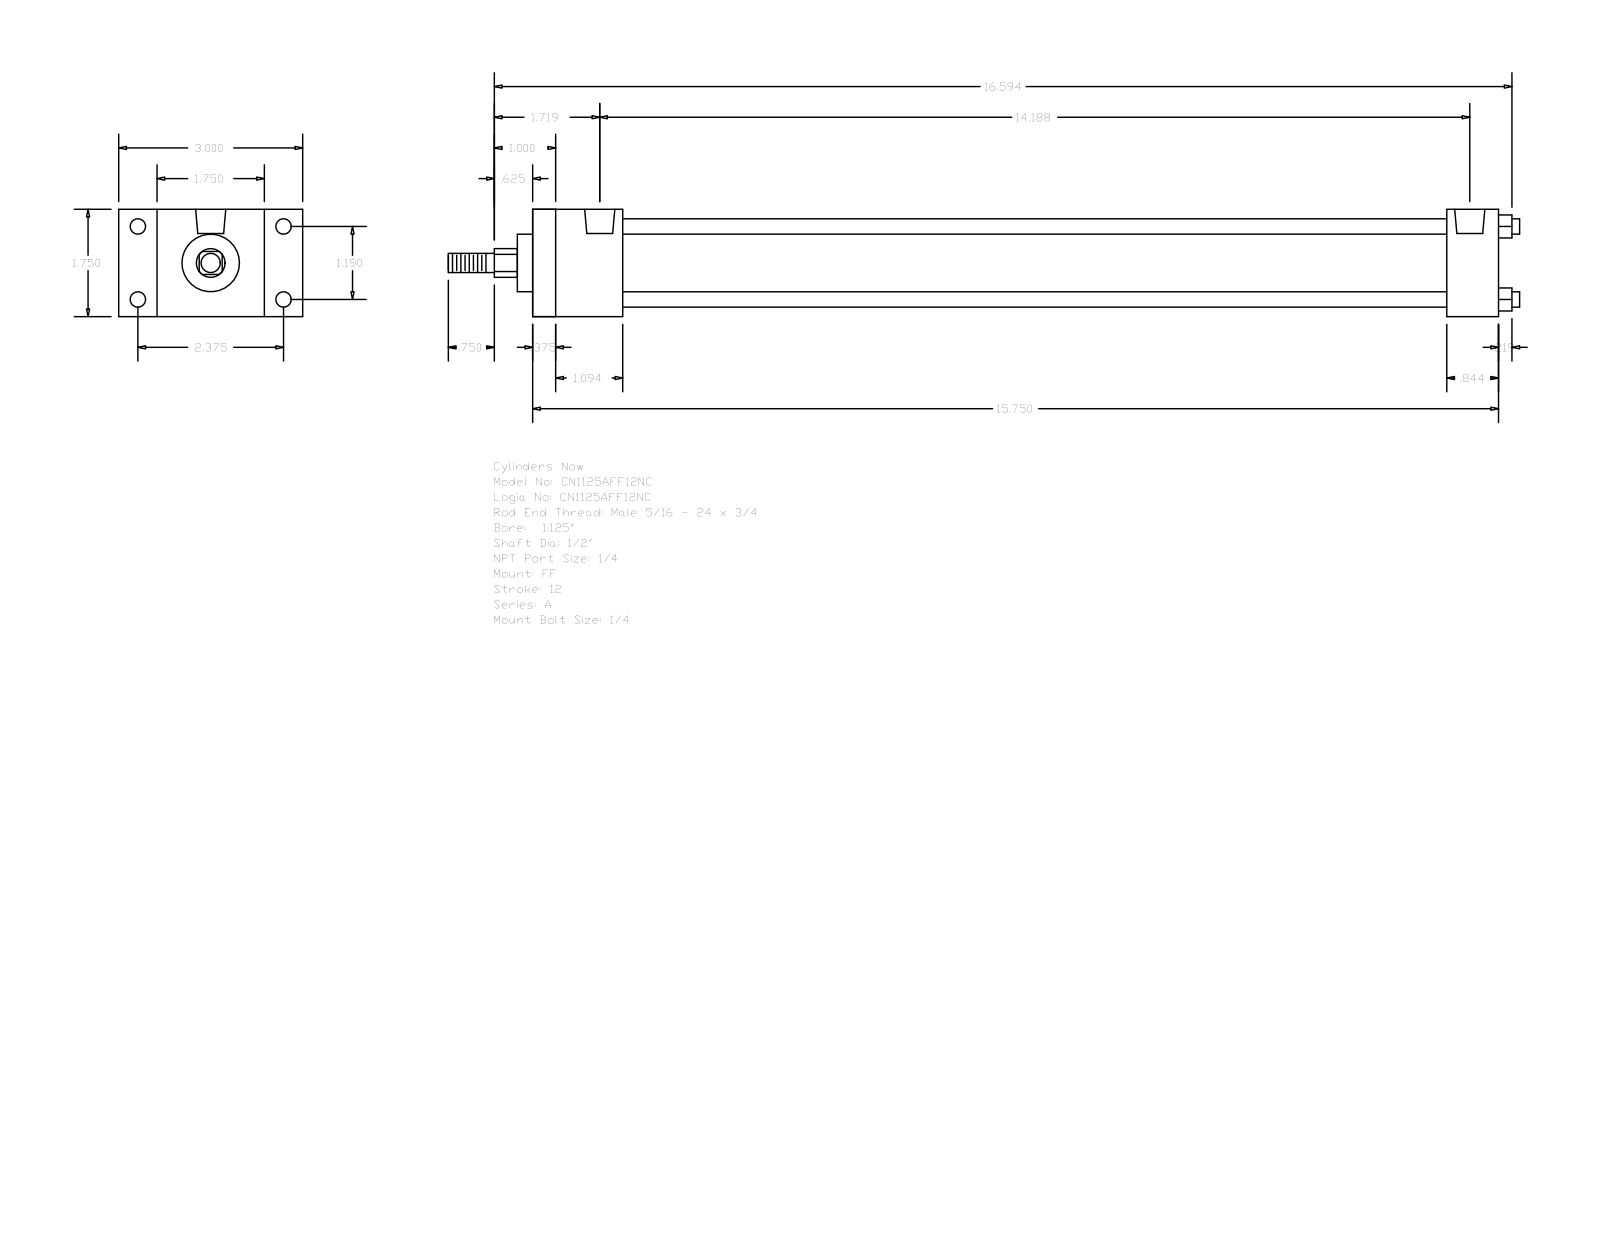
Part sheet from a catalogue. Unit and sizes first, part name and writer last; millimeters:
Units: millimetres
Overall size (bounding box): 443.71 × 76.2 × 44.45
Round holes (diameter × count): ⌀5.56 ×4, ⌀6.35 ×4, ⌀12.49 ×2
Round bosses / shafts (diameter × count): ⌀6.35 ×4, ⌀31.88 ×1, ⌀23.81 ×1, ⌀12.7 ×1, ⌀7.94 ×1
Partial cylindrical surfaces — rounded edges, fillets, slot ends (radius × count): R5.94 ×1
Main face-to-face distances: 44.46, 400.05, 9.52, 390.53, 15.87, 378.61, 369.09, 21.44, 37.3, 27.78
Hole centre spacings: 30.22, 60.32, 67.47, 357.19, 1.58, 1.59, 358.77, 358.78
Bodies: 0 solids, 92 faces (64 planar, 28 cylindrical, 0 other)
Part name (STEP PRODUCT): A_FF__0112_0.5
STEP written by: GSSL Pune (CONFIG_CONTROL_DESIGN)
